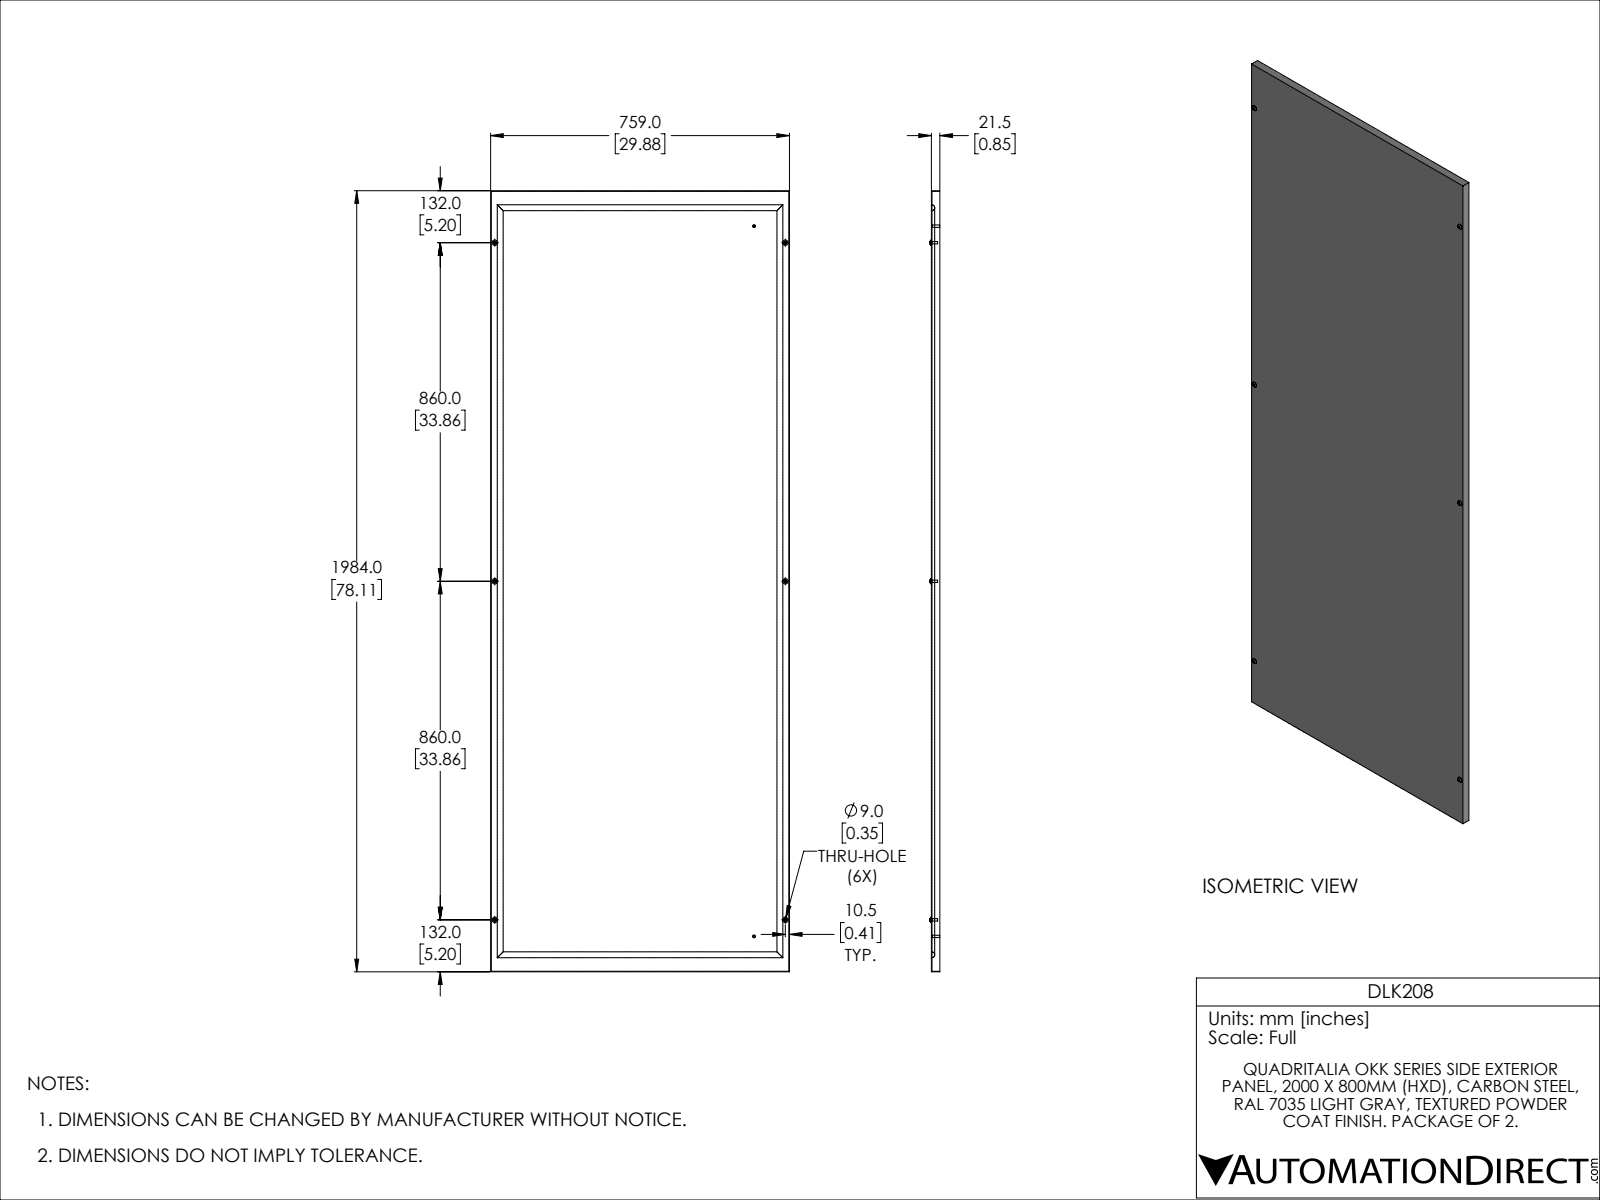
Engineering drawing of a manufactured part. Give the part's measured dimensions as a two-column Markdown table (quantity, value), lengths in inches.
| quantity | value |
| --- | --- |
| part name | DLK208 |
| STEP written by | SolidWorks 2021 (CONFIG_CONTROL_DESIGN) |
| units | inches |
| bodies | 13 solids, 243 faces (125 planar, 98 cylindrical, 20 other) |
| overall size | 78.11 × 29.882 × 0.992 |
| volume | 174 in³ |
| surface area | 5 333 in² |
| round holes (diameter × count) | 0.354 × 6 |
| round bosses / shafts (diameter × count) | 0.236 × 8, 0.551 × 6, 0.276 × 2 |
| partial cylindrical surfaces (radius × count) | 0.02 × 72, 0.296 × 4 |
| main face-to-face distances | 0.059, 29.823, 29.882, 29.764, 78.051, 78.11, 77.992, 0.846, 0.787, 33.039 |
| hole center spacings | 33.858, 44.616, 29.055, 67.717, 73.687 |
